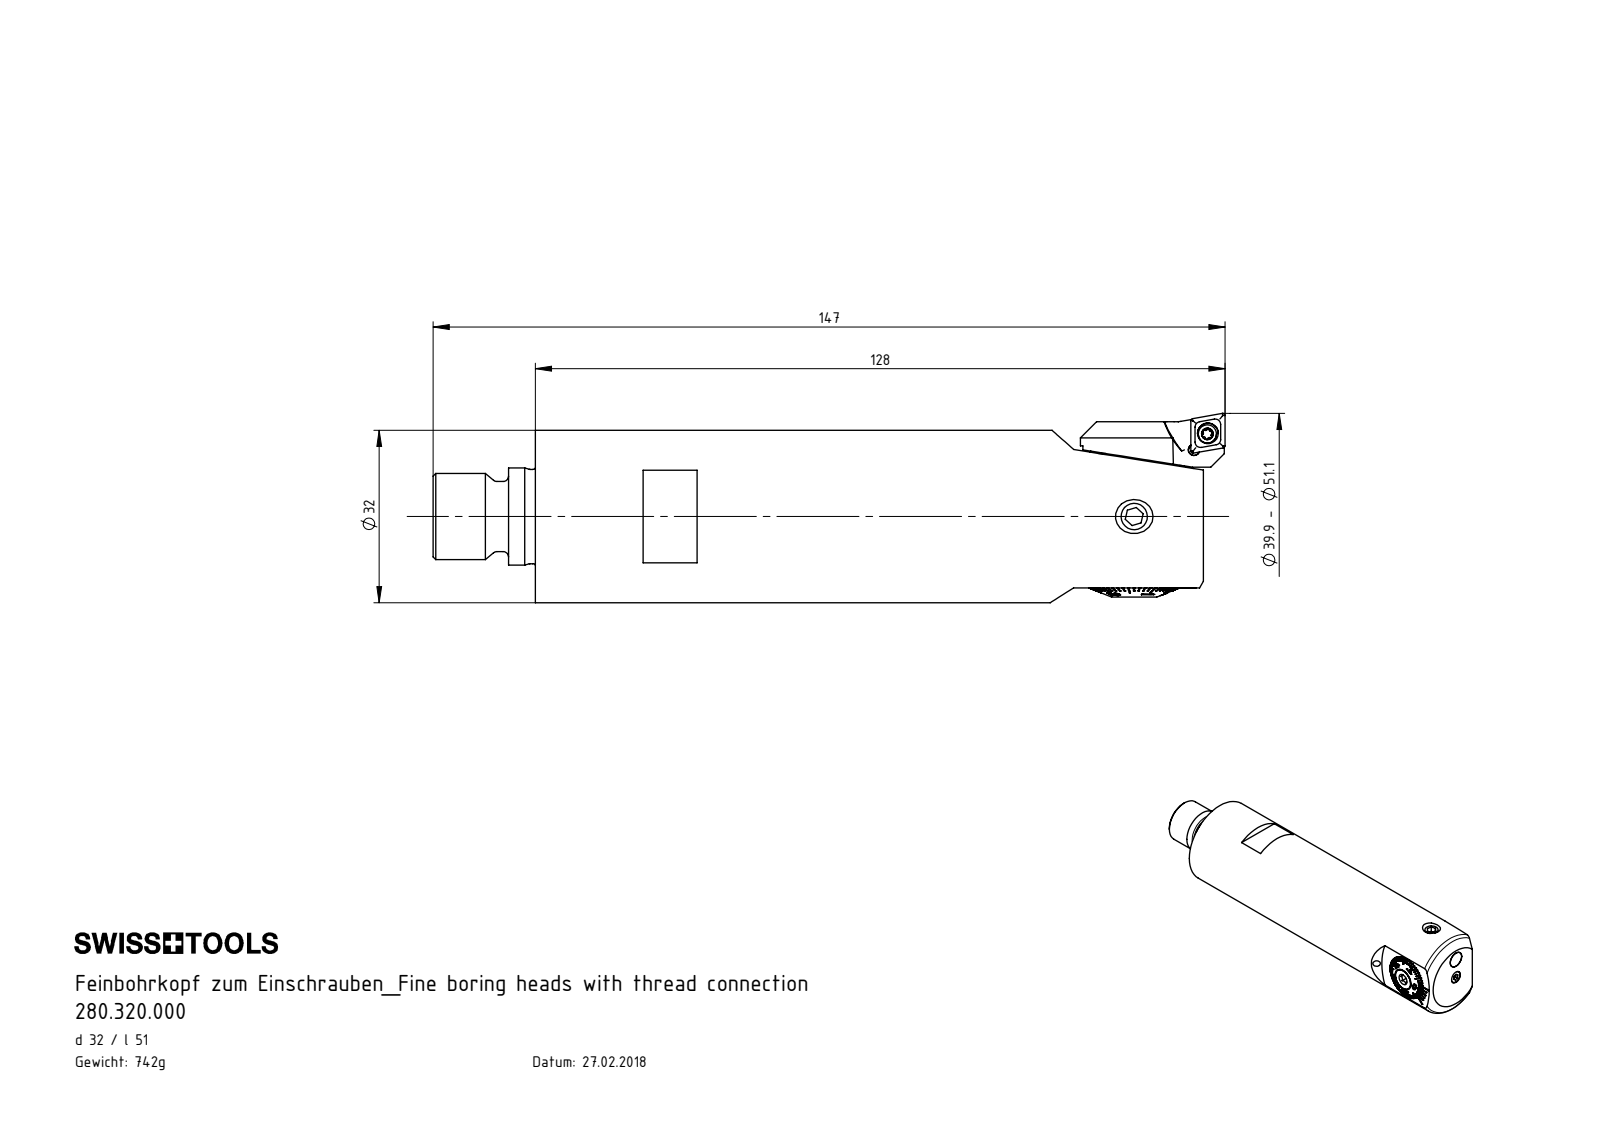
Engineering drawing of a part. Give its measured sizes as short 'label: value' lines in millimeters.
name: ISO 4026 - M6 x 5; CCMT060204; F32-BG2.017.003_A; T7 M2.5 x 6 (+8 more)
written by: SolidWorks 2022 (AUTOMOTIVE_DESIGN)
unit: mm
bodies: 16 solids, 790 faces (337 planar, 149 cylindrical, 304 other)
size: 147 × 35.85 × 32
volume: 96 900 mm³; area: 26 756 mm²
holes: 4× ⌀2.5, 2× ⌀5, 1× ⌀2, 1× ⌀2.05, 1× ⌀2.1, 1× ⌀2.7, 1× ⌀2.8, 1× ⌀2.9, 1× ⌀3, 1× ⌀3.85, 1× ⌀6, 1× ⌀6.5
bosses: 2× ⌀6, 2× ⌀2.5, 1× ⌀32, 1× ⌀18, 1× ⌀17.5, 1× ⌀16.98, 1× ⌀16.85, 1× ⌀16
rounds: 6× R0.21, 4× R0.36, 4× R0.5, 2× R0.36, 2× R1.75, 1× R1, 1× R1.9, 1× R3.2
face distances: 124, 0.8, 4.4, 26.05, 25.25, 1.5, 5.2, 4.5, 27, 23.75
hole spacings: 3.84, 3.99, 5.7, 8, 11.68
